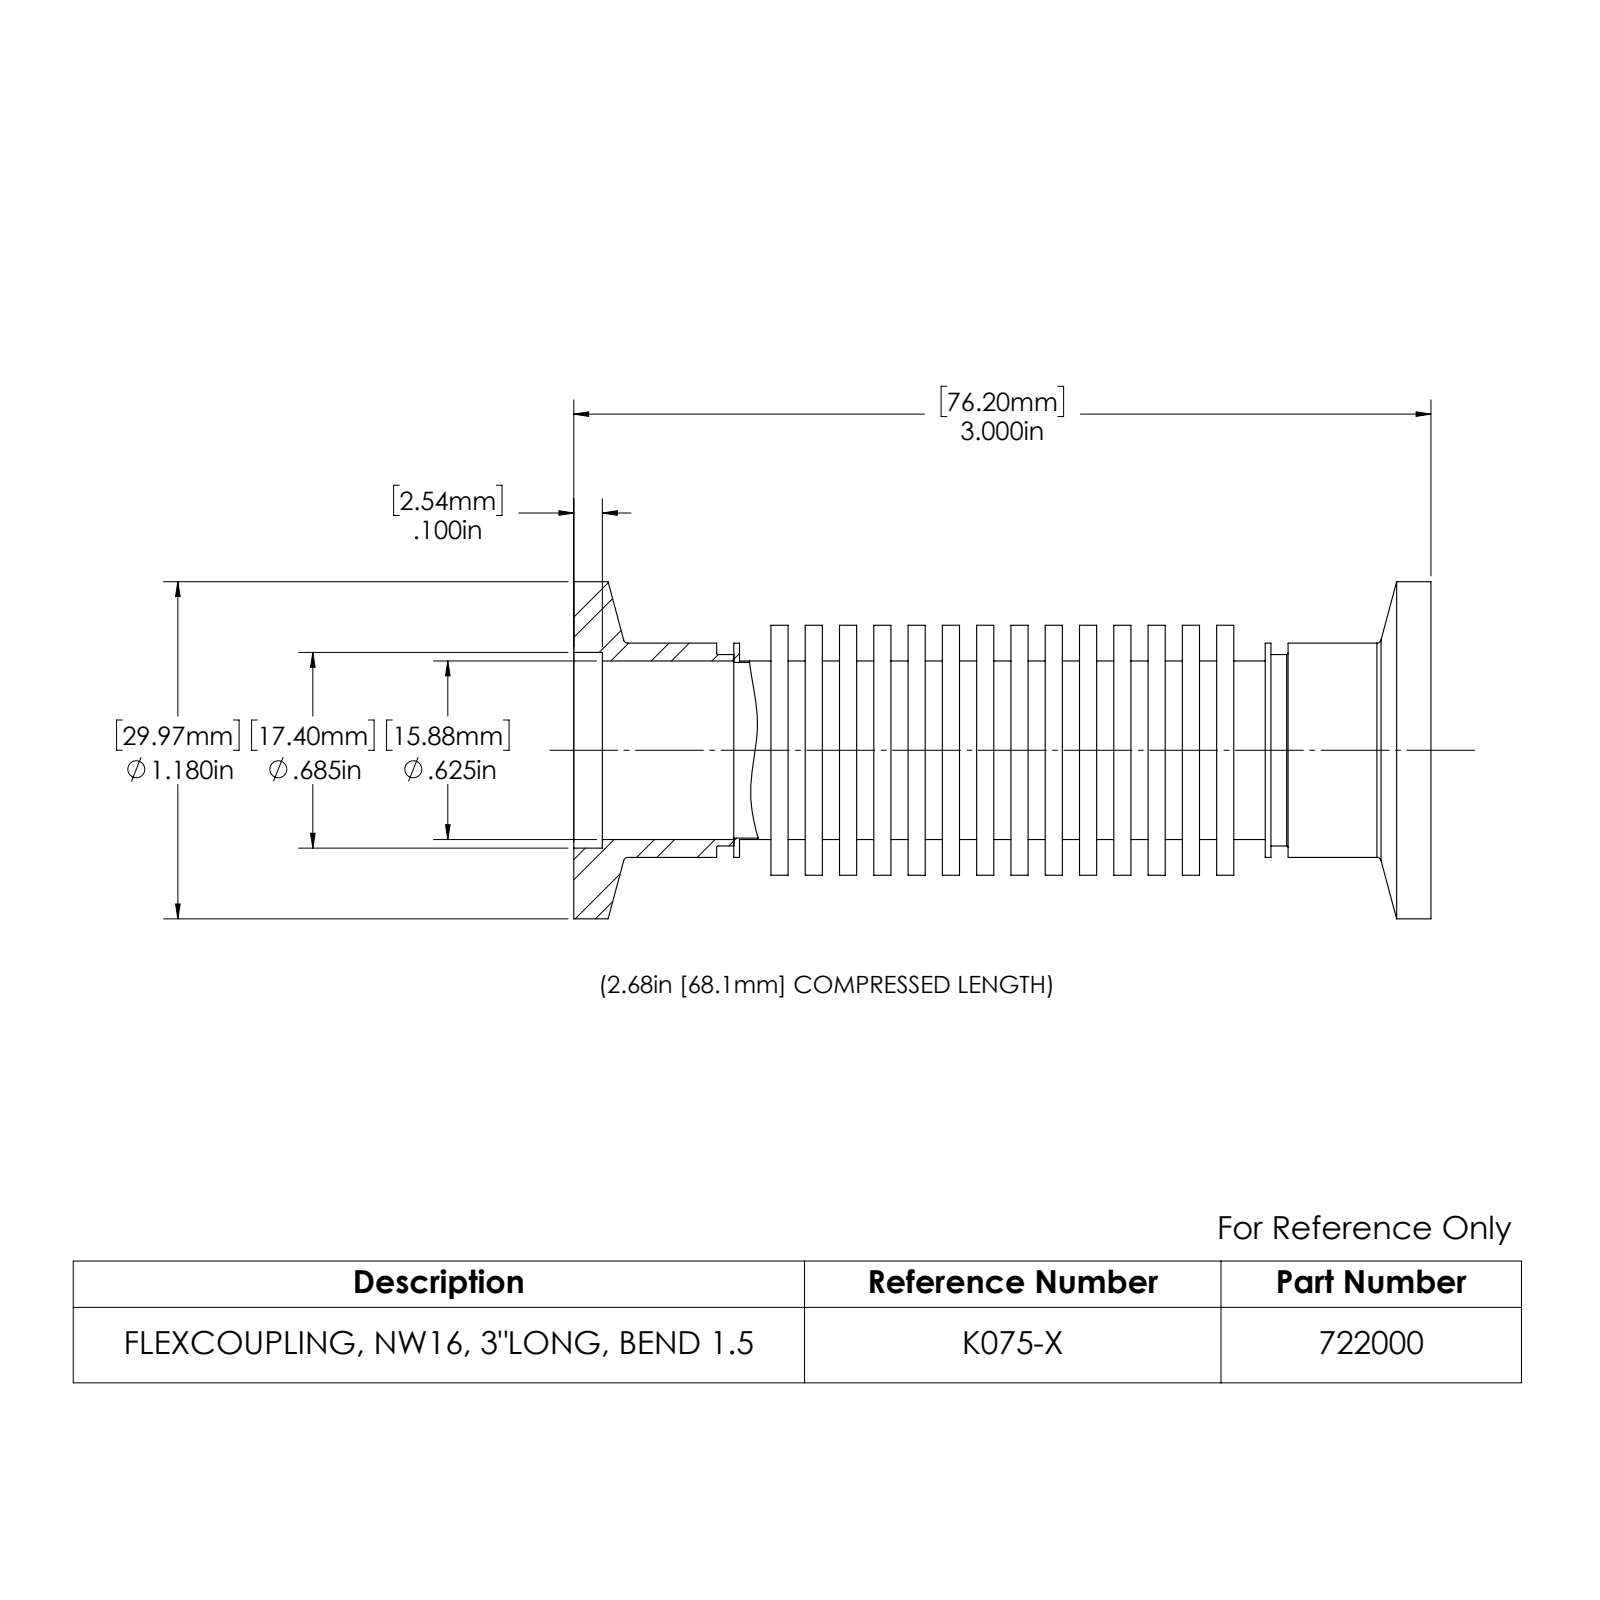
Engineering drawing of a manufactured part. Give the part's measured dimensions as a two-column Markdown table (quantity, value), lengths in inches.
| quantity | value |
| --- | --- |
| part name | 713001; 722000_A; SUB1 |
| STEP written by | SolidWorks 2022 (CONFIG_CONTROL_DESIGN) |
| units | inches |
| bodies | 3 solids, 704 faces (176 planar, 32 cylindrical, 496 other) |
| overall size | 3 × 1.18 × 1.18 |
| volume | 0.458 in³ |
| surface area | 61.8 in² |
| round holes (diameter × count) | 0.615 × 1, 0.625 × 1, 0.685 × 1 |
| round bosses / shafts (diameter × count) | 1.18 × 1, 0.75 × 1, 0.67 × 1, 0.625 × 1 |
| main face-to-face distances | 0.08, 0.12, 0.2, 0.04, 0.28, 0.16, 0.24, 0.32, 0.04, 0.16 |
